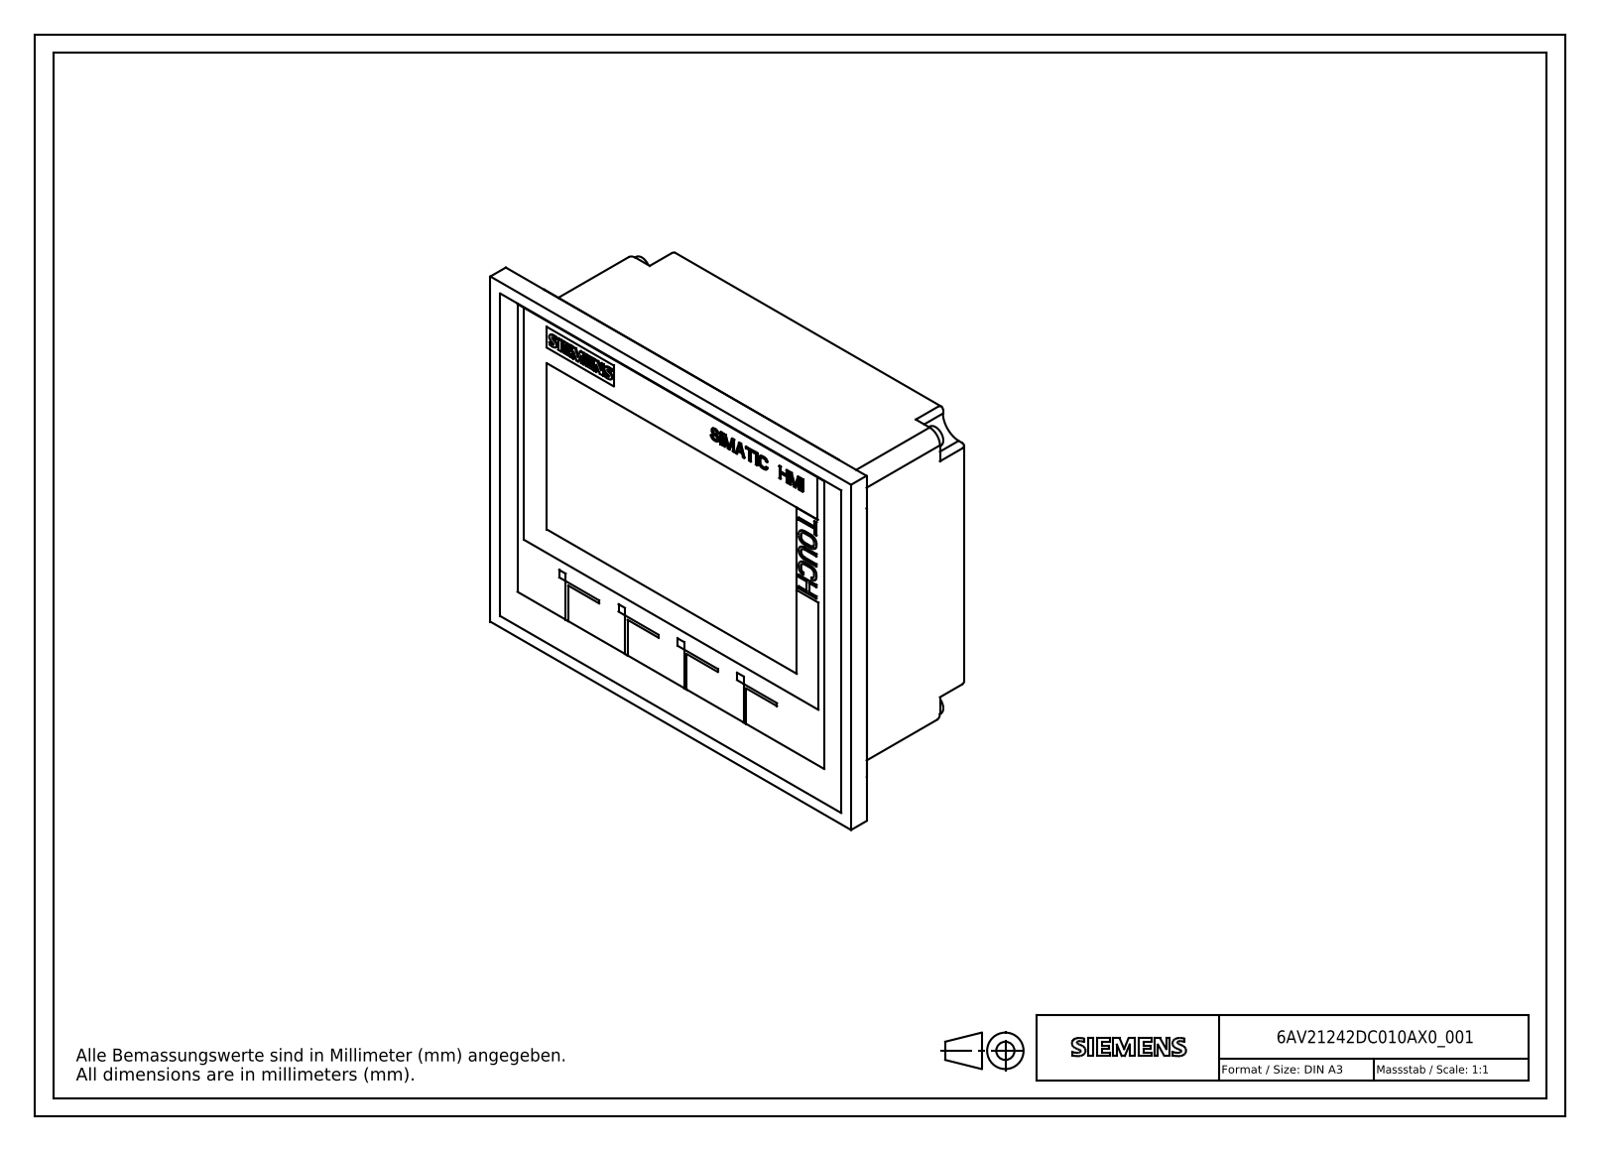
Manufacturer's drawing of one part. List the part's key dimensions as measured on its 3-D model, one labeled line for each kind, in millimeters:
Part name (STEP PRODUCT): A5E30292383A_001; A5E30291496A_001; A5E30291494A_001; A5E30291499A_001
STEP written by: SIEMENS UGS NX 6.0 (AUTOMOTIVE_DESIGN)
Units: millimetres
Bodies: 212 solids, 2356 faces (1976 planar, 140 cylindrical, 240 other)
Overall size (bounding box): 140 × 116 × 54.1
Volume: 621 400 mm³ · Surface area: 104 821 mm²
Round holes (diameter × count): ⌀0.9 ×9, ⌀2.4 ×2
Round bosses / shafts (diameter × count): ⌀6 ×4, ⌀3 ×2, ⌀0.96 ×2, ⌀0.8 ×2, ⌀8 ×1, ⌀5.5 ×1
Partial cylindrical surfaces — rounded edges, fillets, slot ends (radius × count): R0.2 ×53, R0.1 ×6, R0.85 ×6, R0.45 ×4, R1.85 ×4, R2 ×4, R2.02 ×4, R3.96 ×4
Main face-to-face distances: 48, 52.92, 4.92, 53.58, 5.58, 0.66, 9, 94, 53.66, 5.66
Hole centre spacings: 3.07, 2.76, 4.96, 5.52, 7.42, 8.28, 7.11, 8.47
